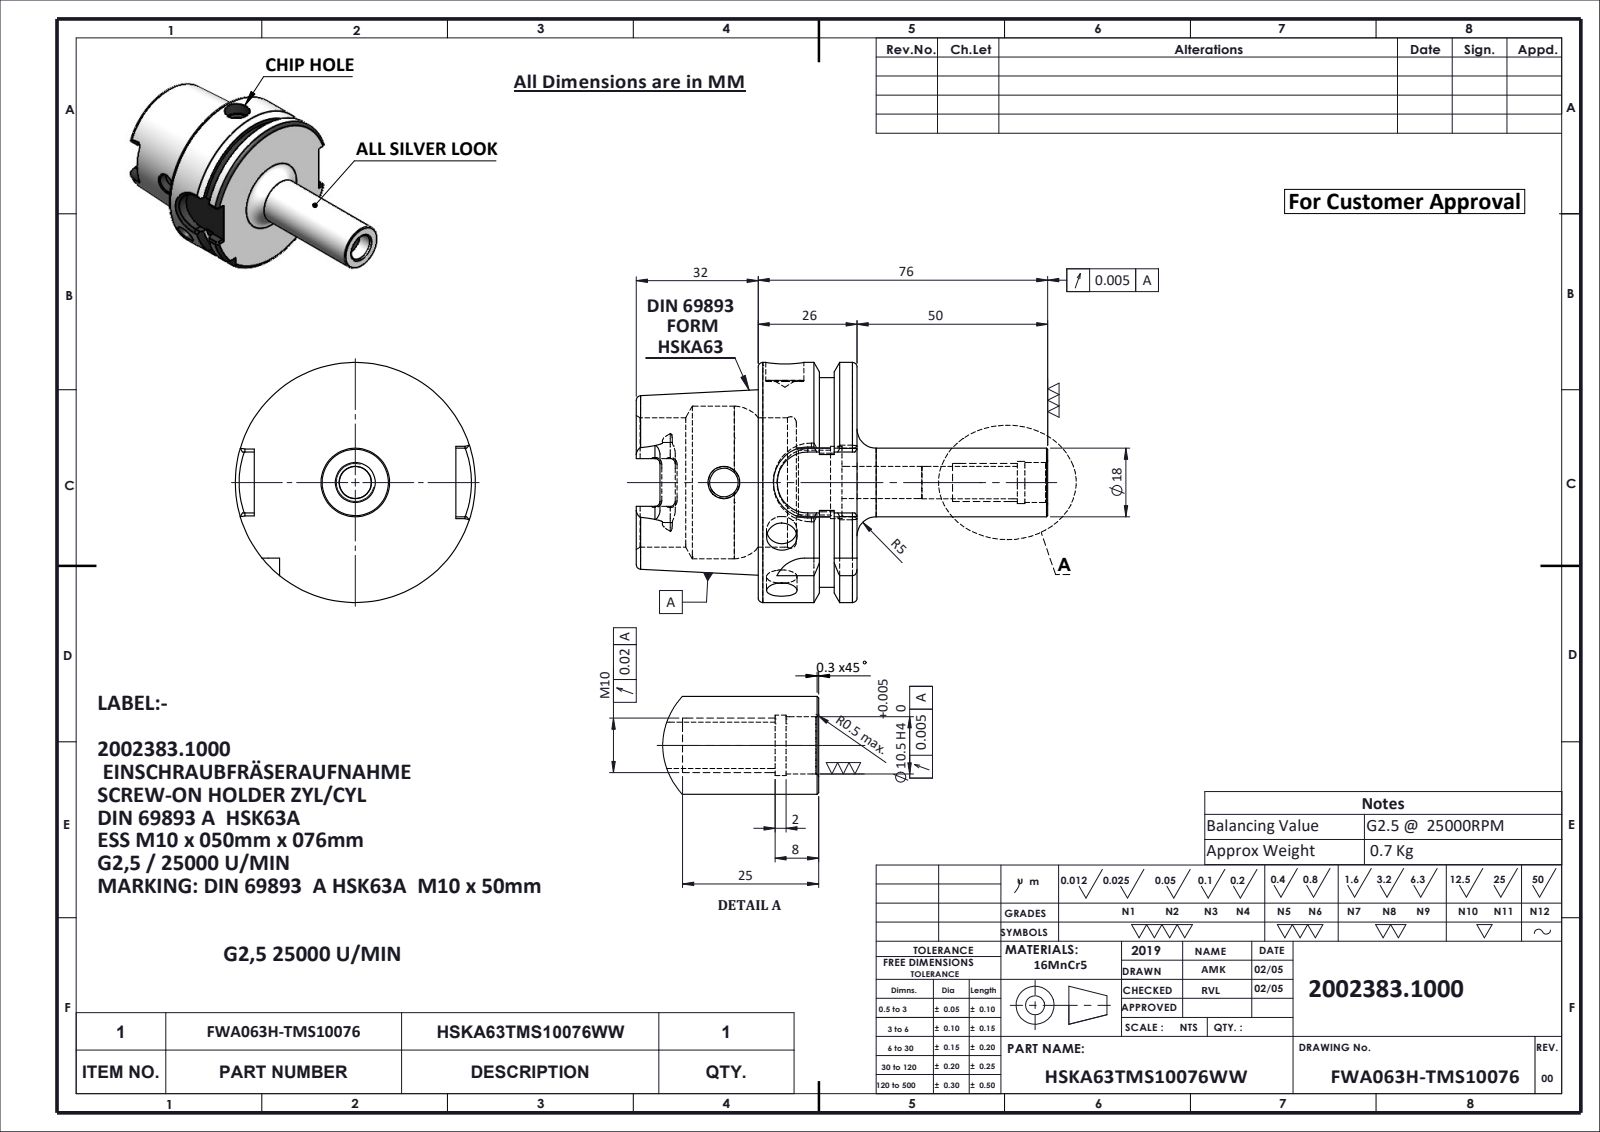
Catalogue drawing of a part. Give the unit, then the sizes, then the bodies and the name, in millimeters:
Units: millimetres
Overall size (bounding box): 108 × 63 × 63
Round holes (diameter × count): ⌀8 ×2, ⌀7.5 ×1, ⌀8.4 ×1, ⌀8.5 ×1, ⌀10 ×1, ⌀10.5 ×1, ⌀11.1 ×1, ⌀17 ×1, ⌀19 ×1, ⌀34 ×1, ⌀40 ×1
Round bosses / shafts (diameter × count): ⌀63 ×1, ⌀55 ×1, ⌀18 ×1
Partial cylindrical surfaces — rounded edges, fillets, slot ends (radius × count): R1.3 ×6, R2.88 ×4, R8 ×2, R9 ×1
Main face-to-face distances: 25.95, 10, 15.95, 32, 42, 57.95, 54, 52.9, 22, 12
Volume: 90 807 mm³ · Surface area: 26 446 mm²
Bodies: 1 solid, 168 faces (51 planar, 53 cylindrical, 64 other)
Part name (STEP PRODUCT): FWA063H-TMS10076; HSKA63TMS10076WW
STEP written by: SolidWorks 2024 (CONFIG_CONTROL_DESIGN)
